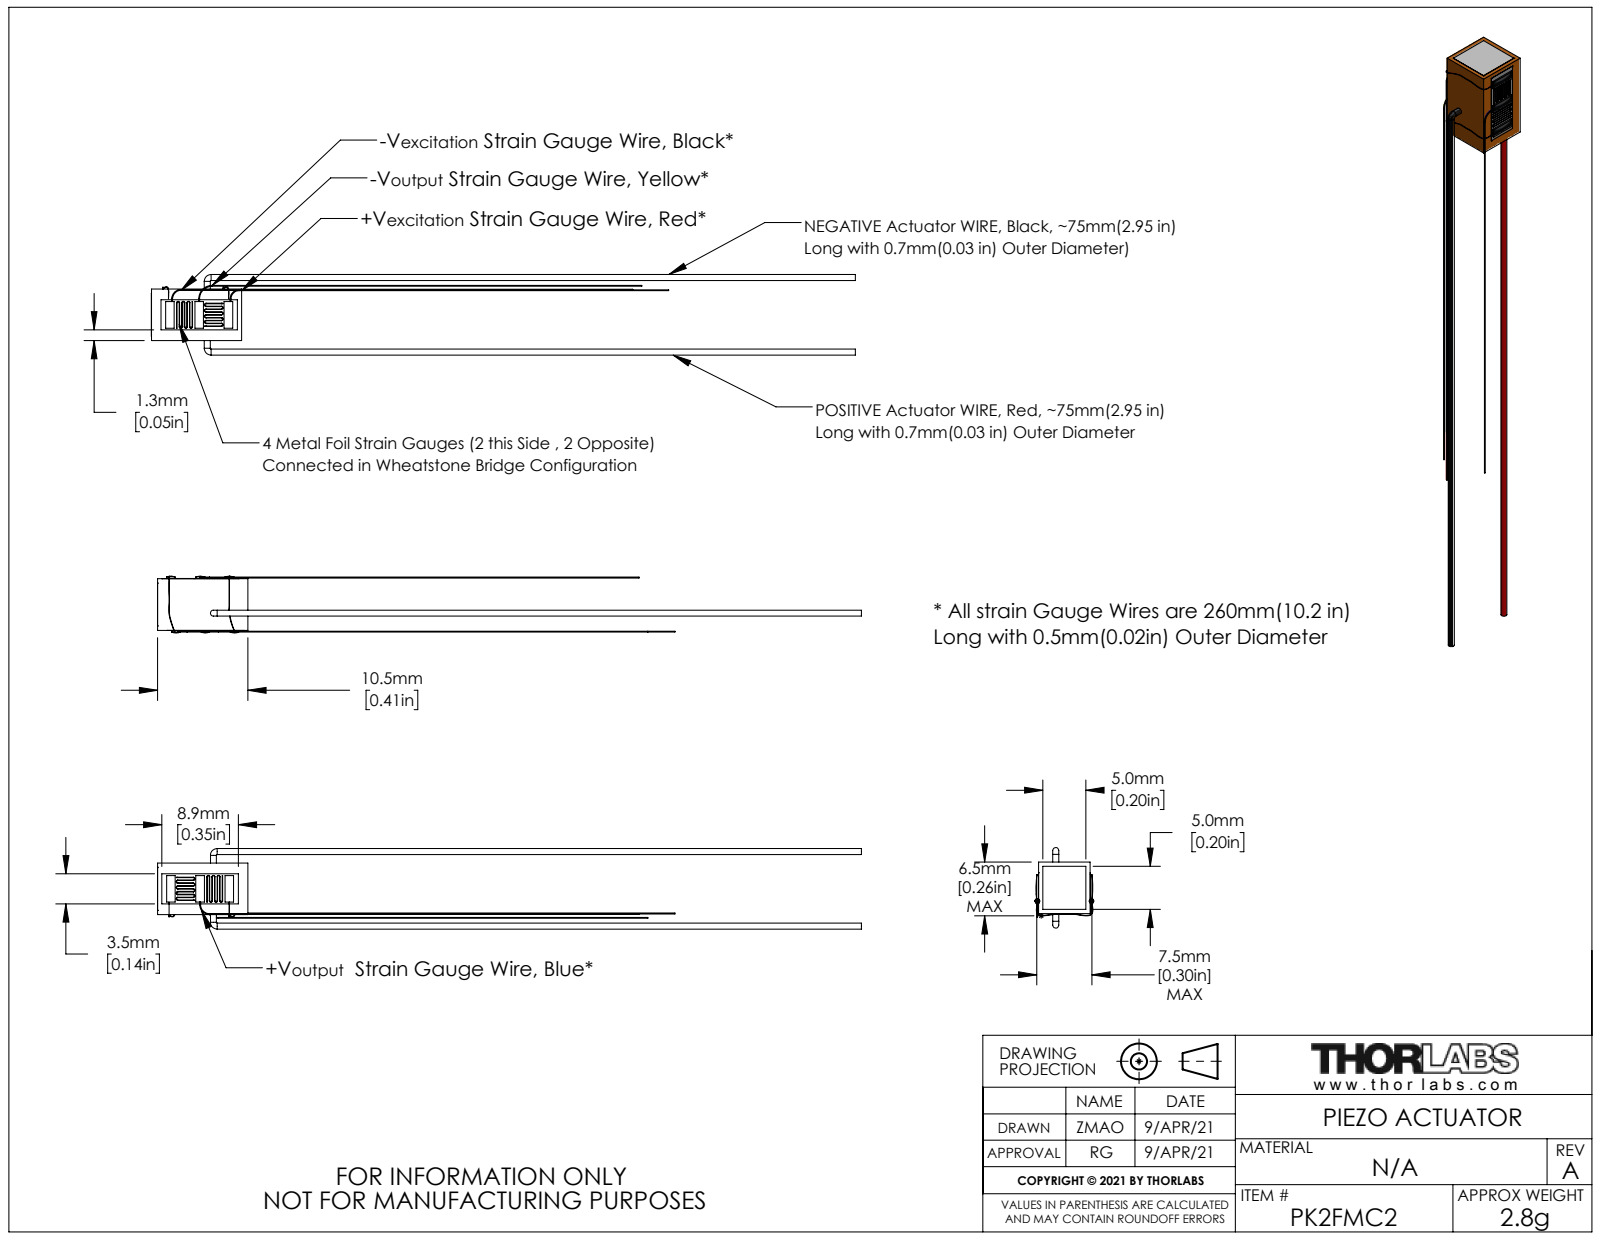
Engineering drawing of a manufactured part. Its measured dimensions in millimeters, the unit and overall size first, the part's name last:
Units: millimetres
Overall size (bounding box): 81.95 × 9.38 × 6.63
Round bosses / shafts (diameter × count): ⌀0.7 ×3
Main face-to-face distances: 6, 6.01, 10.5, 6.02, 10.51, 10.49, 3.4, 0.6, 1, 6.8
Volume: 444 mm³ · Surface area: 731 mm²
Bodies: 2 solids, 186 faces (69 planar, 65 cylindrical, 52 other)
Part name (STEP PRODUCT): CTN016916-E0W
STEP written by: SolidWorks 2018 (AUTOMOTIVE_DESIGN)
